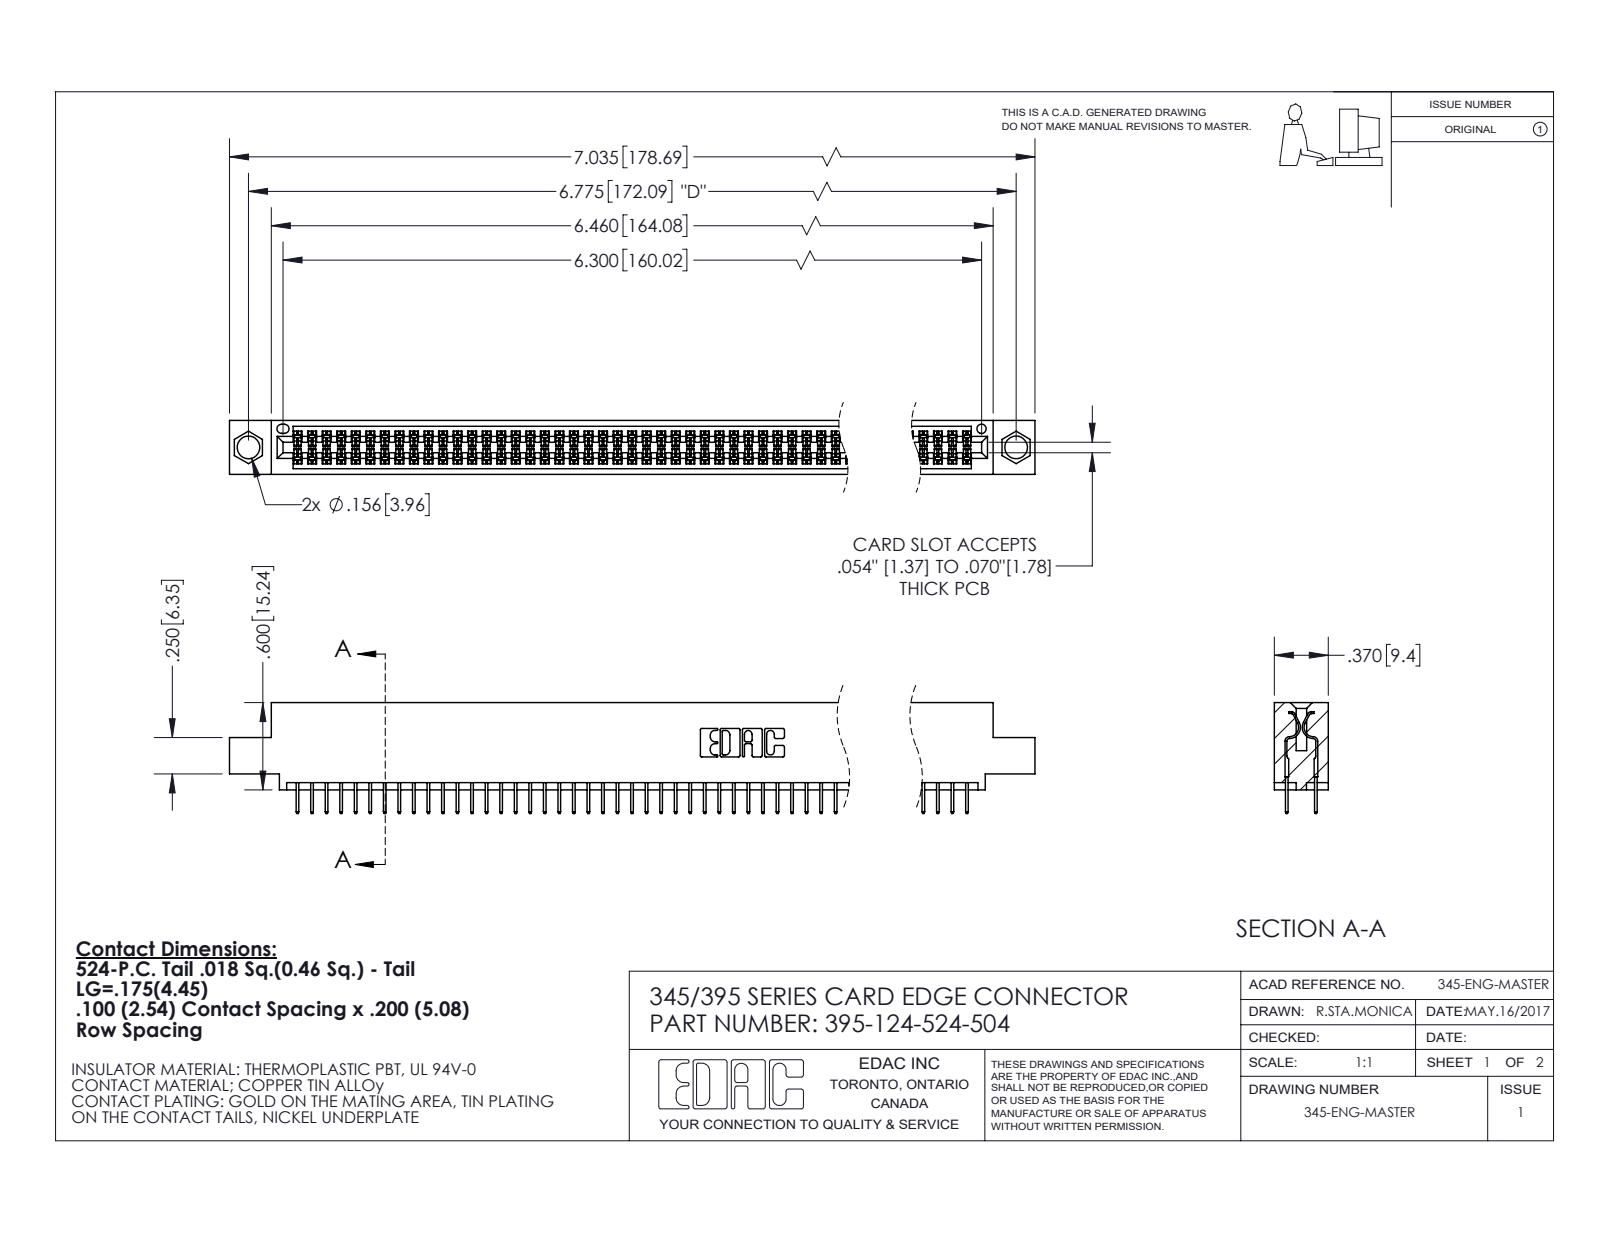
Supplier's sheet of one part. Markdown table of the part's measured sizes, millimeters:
| quantity | value |
| --- | --- |
| part name | 345-292-001_345-293-124; 395-124-524-504; 345 Part_0.110 Offset - 0.156 Dia-TI |
| STEP written by | SolidWorks 2020 (CONFIG_CONTROL_DESIGN) |
| units | millimeters |
| bodies | 125 solids, 6840 faces (4934 planar, 1906 cylindrical, 0 other) |
| overall size | 178.7 × 19.4 × 9.4 |
| volume | 17 170 mm³ |
| surface area | 25 230 mm² |
| round holes (diameter × count) | 4 × 2, 1.6 × 1 |
| partial cylindrical surfaces (radius × count) | 0.2 × 248, 0.3 × 22, 0.2 × 6, 0.8 × 6, 0.7 × 3, 0.4 × 2, 0.5 × 2, 0.6 × 2 |
| main face-to-face distances | 1.8, 7.6, 5.1, 9.4, 2.5, 6.9, 0.6, 5.7, 1.8, 4.4 |
| hole center spacings | 6.9, 166.1, 172.1 |
